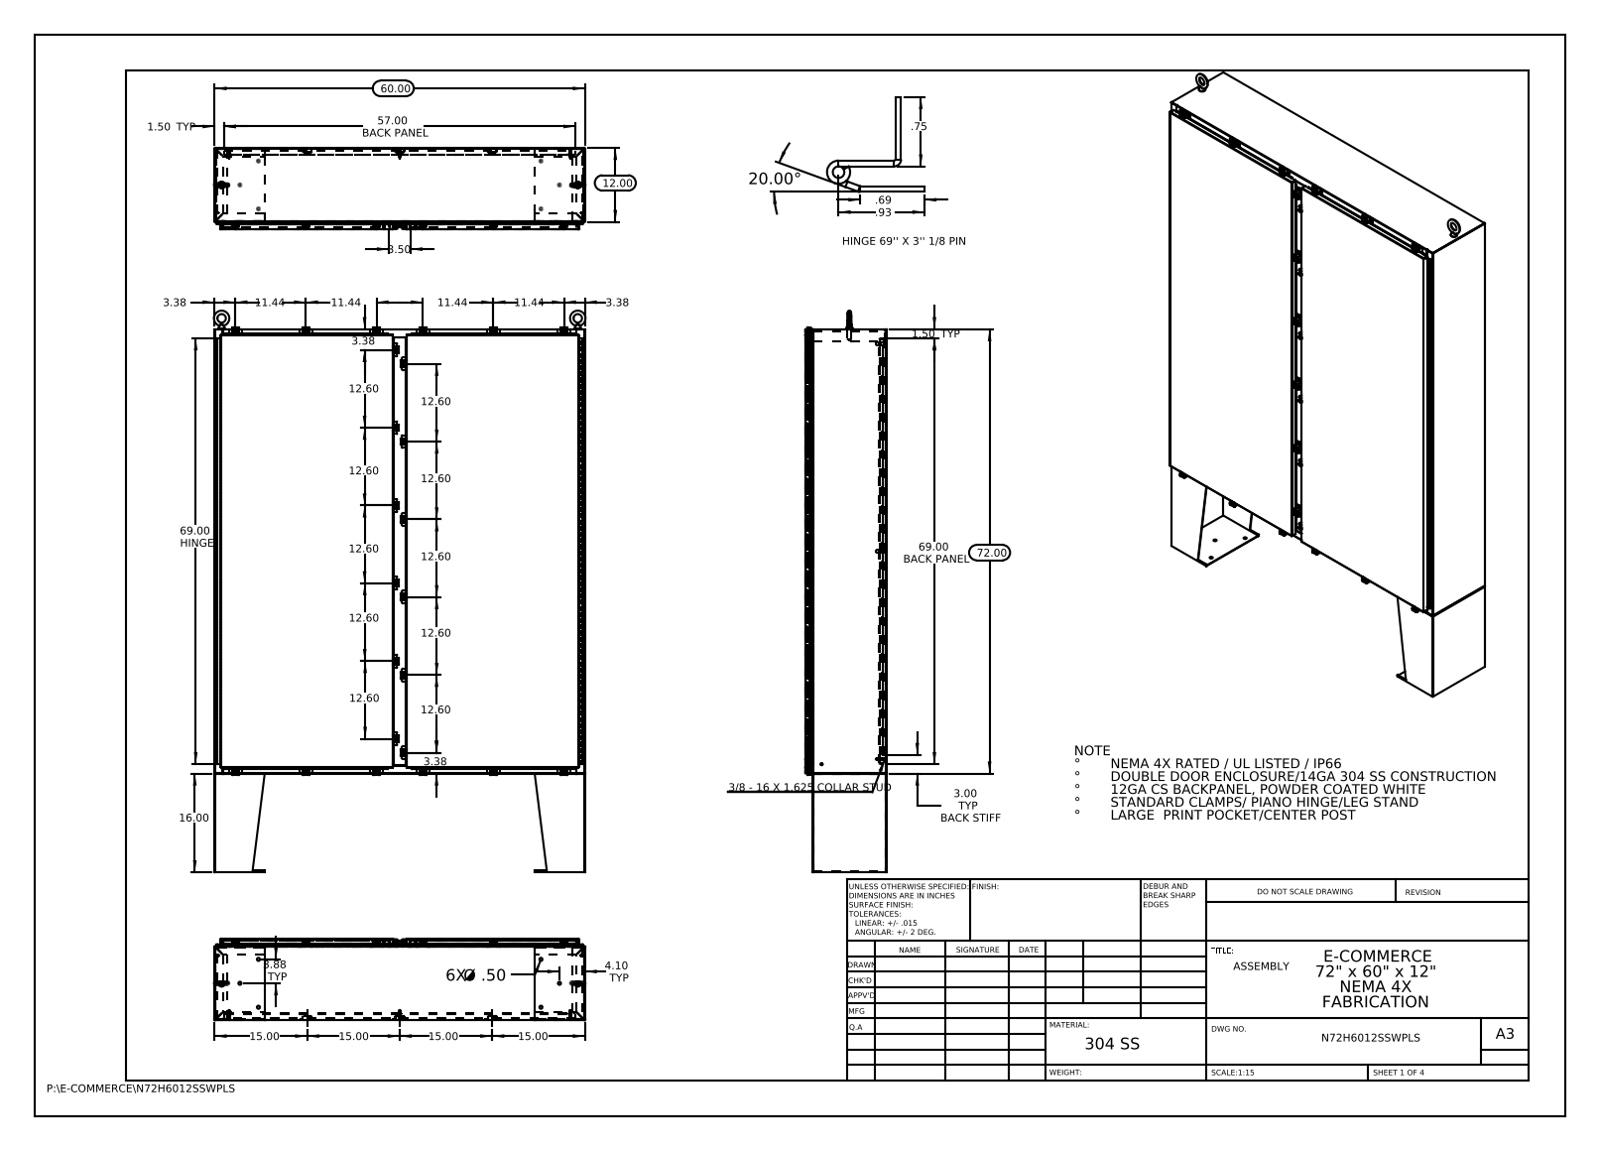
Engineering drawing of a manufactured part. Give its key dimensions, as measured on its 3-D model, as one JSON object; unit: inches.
{"part_name": "N72H6012SSWPLS; Standard Clamps; N72H6012SSWPLS Center Post; N72H6012SSWPLS Hinge Cover Side DoubleDoor (+8 more)", "step_written_by": "SolidWorks 2013 (CONFIG_CONTROL_DESIGN)", "units": "inches", "bodies": {"solids": 154, "faces": 7158, "planar": 3714, "cylindrical": 3100, "other": 344}, "overall_size": [91, 60.226, 13.201], "volume_in3": 1592, "surface_area_in2": 38664, "round_holes": [[0.26, 26], [0.213, 24], [0.5, 14], [0.75, 4], [0.125, 2], [0.125, 2]], "round_bosses_or_shafts": [[0.5, 26], [0.25, 26], [0.399, 24], [0.625, 10], [0.375, 8], [0.33, 8], [0.315, 3], [0.236, 3]], "partial_cylinders_radius": [[0.06, 104], [0.013, 48], [0.12, 48], [0.141, 48], [0.088, 40], [0.05, 36], [0.08, 36], [0.09, 36]], "face_to_face_distances": [0.075, 13.126, 0.104, 1.075, 13.051, 1, 12.126, 1.179, 1.104, 12.051], "hole_center_spacings": [72.341, 12.6, 71.431, 4.293, 7.117, 7.137, 10.433, 11.437]}
